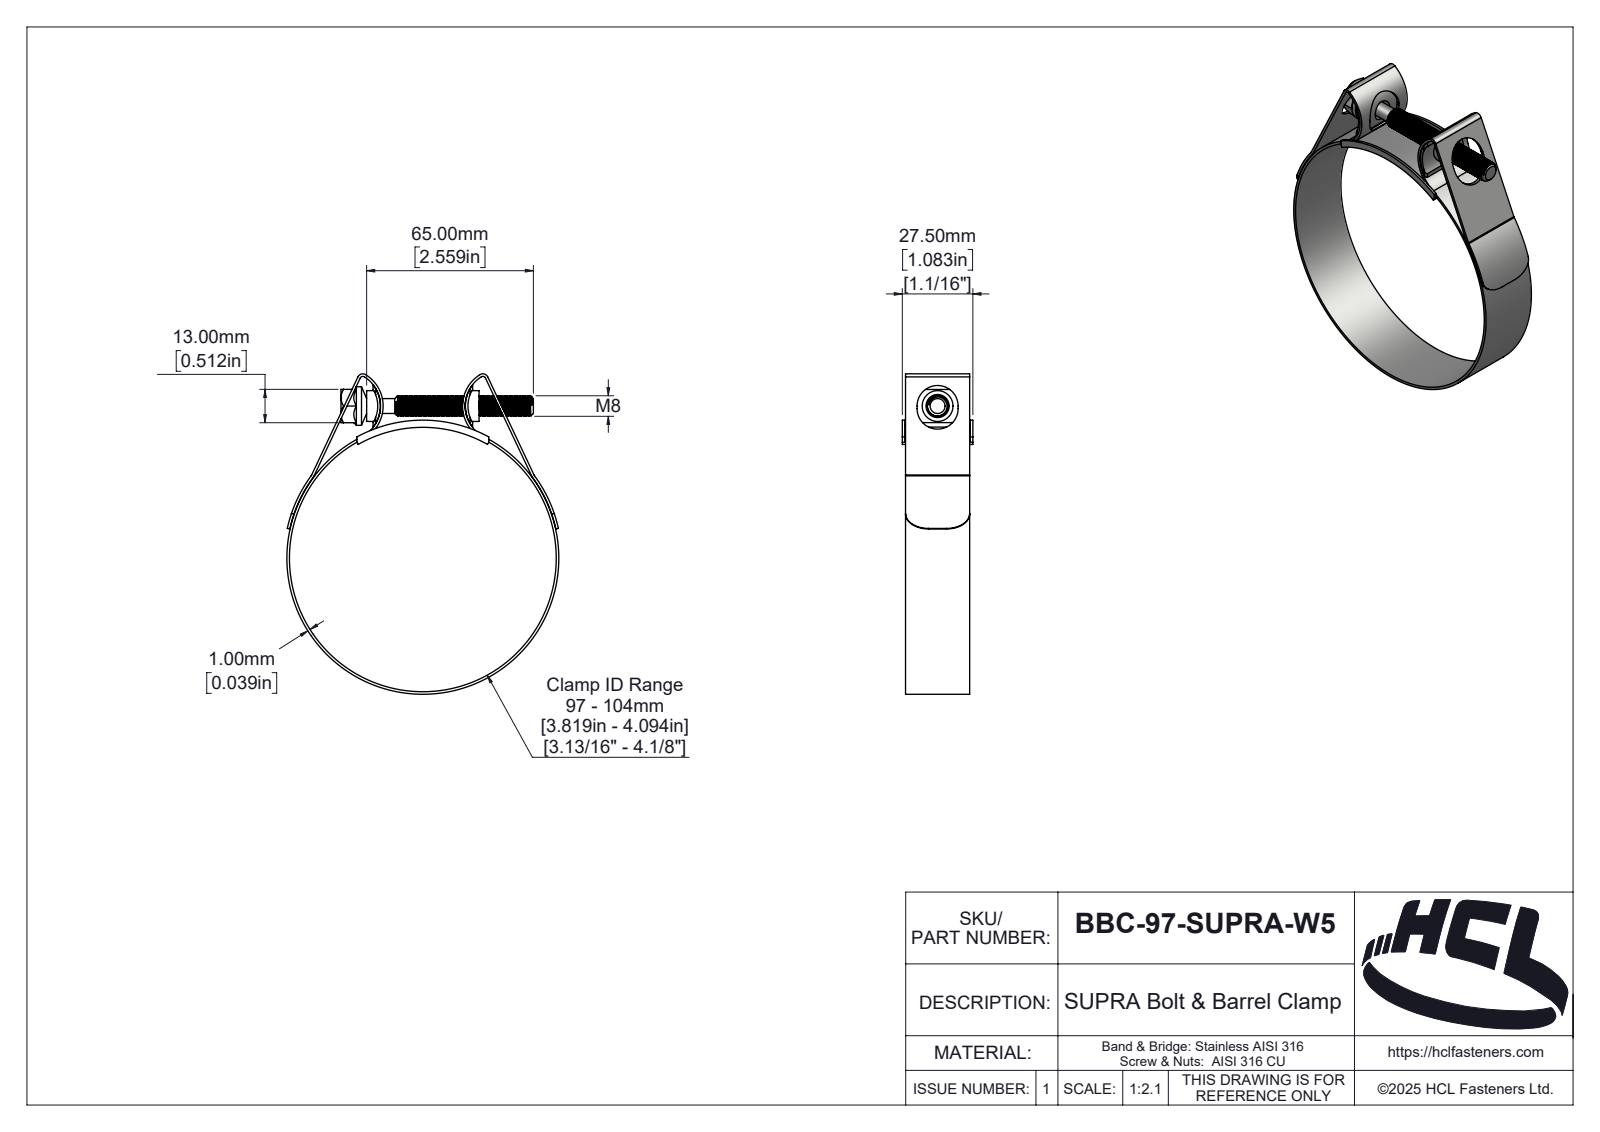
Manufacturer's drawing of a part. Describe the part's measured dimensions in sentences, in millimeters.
The part is named "BBC-97-SUPRA-W5". Its 3-D file was written by "SolidWorks 2025 (AUTOMOTIVE_DESIGN)". It is 5 solids with 350 faces: 46 planar, 217 cylindrical and 87 other. Overall it measures 124.85 by 106 by 27.5 millimeters. Its volume is 17 797 cubic millimeters and its surface area 31 528 square millimeters. Round holes: 1 of diameter 104. Round bosses or shafts: 1 of diameter 106, 1 of diameter 15.01, 1 of diameter 12, 1 of diameter 8, 1 of diameter 5.8. Partial cylindrical surfaces (rounded edges, fillets, slot ends): 4 of radius 1, 2 of radius 1.1, 2 of radius 2, 2 of radius 2.1, 2 of radius 3, 2 of radius 8, 2 of radius 12.3, 2 of radius 13.3. The main face-to-face distances are 1, 25, 1.25, 26.25, 26.5, 25.25, 27.5, 13, 2.5, 41.32.
